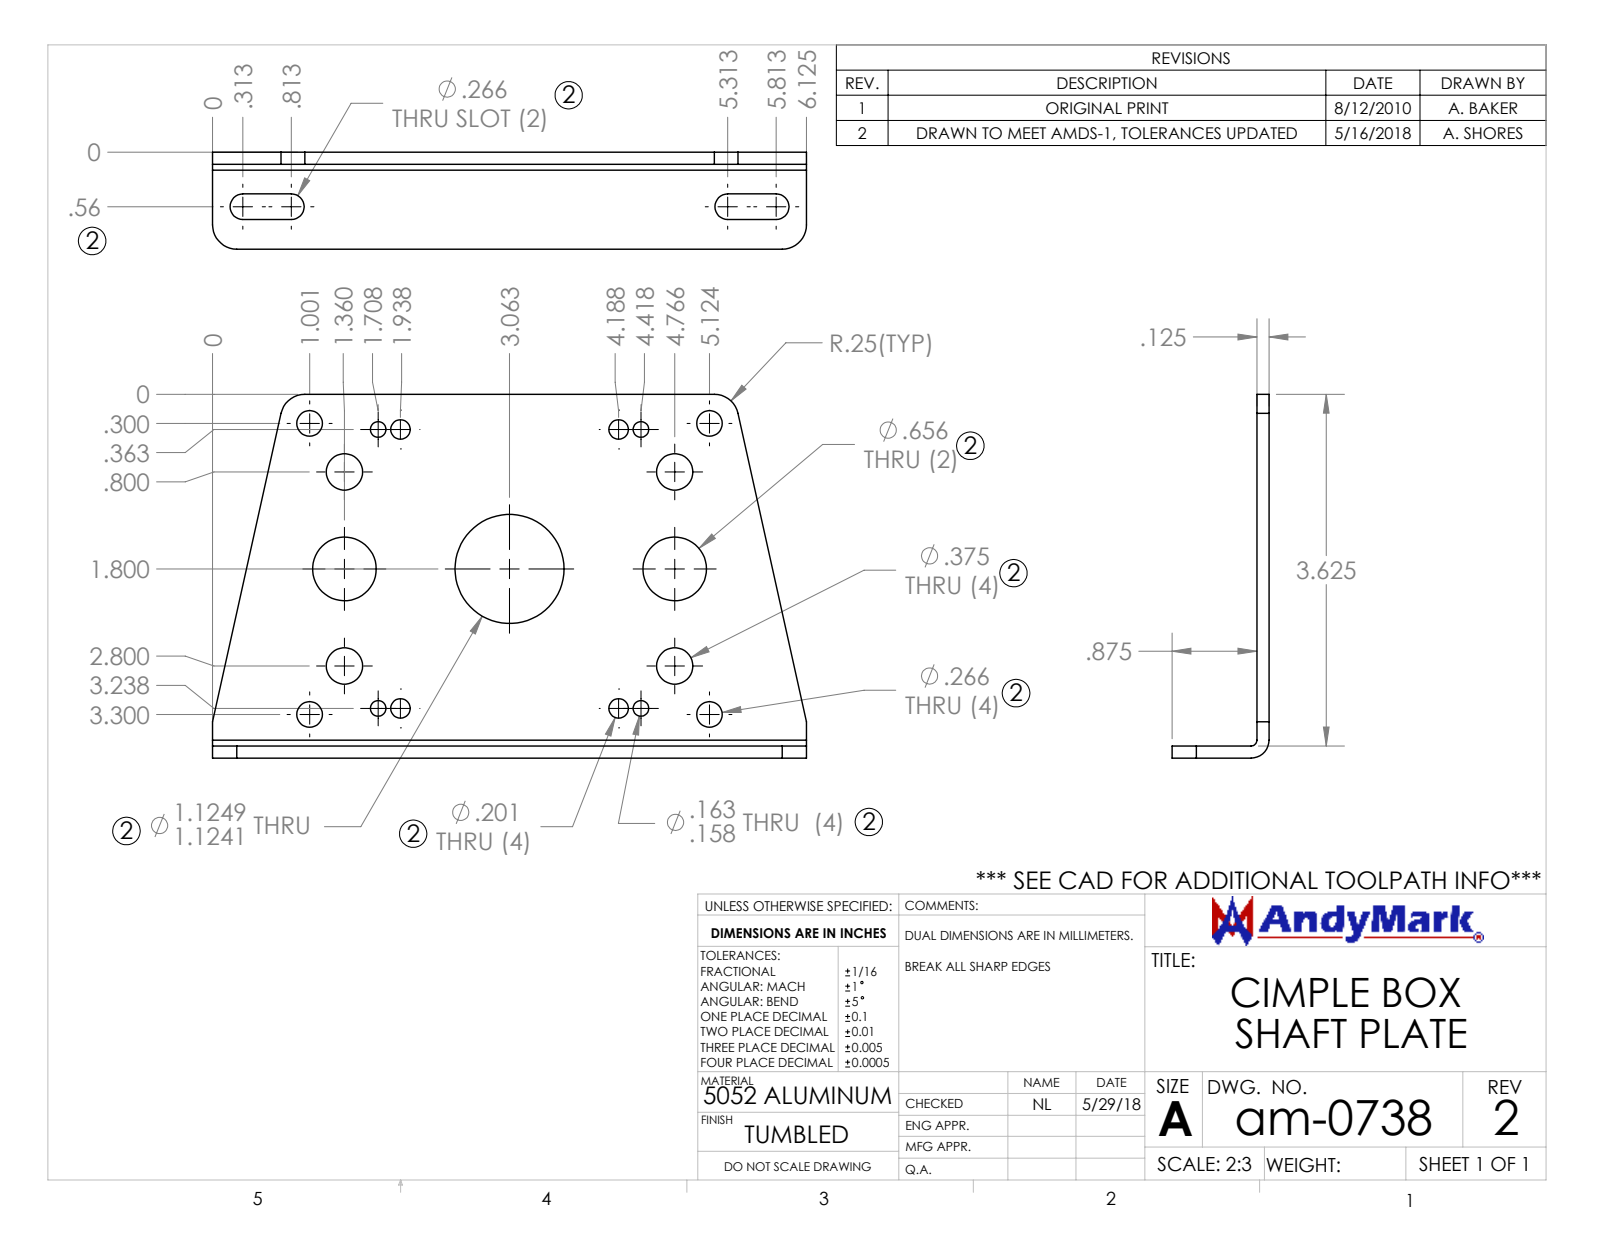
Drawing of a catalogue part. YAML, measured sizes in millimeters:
part_name: "am-0738 CIMple Box Shift Plate REV2"
step_written_by: "SolidWorks 2017 (AUTOMOTIVE_DESIGN)"
units: millimeters
bodies: {solids: 1, faces: 66, planar: 18, cylindrical: 48, other: 0}
overall_size: [155.4, 95.3, 25.4]
volume: 45920
surface_area: 32450
round_holes:
  - {diameter: 4.1, count: 4}
  - {diameter: 5.1, count: 4}
  - {diameter: 6.7, count: 4}
  - {diameter: 9.7, count: 4}
  - {diameter: 16.8, count: 2}
  - {diameter: 28.6, count: 1}
partial_cylinders:
  - {radius: 3.4, count: 4}
  - {radius: 6.4, count: 4}
  - {radius: 0.7, count: 1}
  - {radius: 3.9, count: 1}
face_to_face_distances: [3.2, 25.4, 22.2, 95.3, 92.1, 10.9, 7.7, 14.5, 17.6, 14.5]
hole_center_spacings: [14.2, 23.9, 25.4, 64.2, 73.1, 73.3, 78.3, 80.8]
